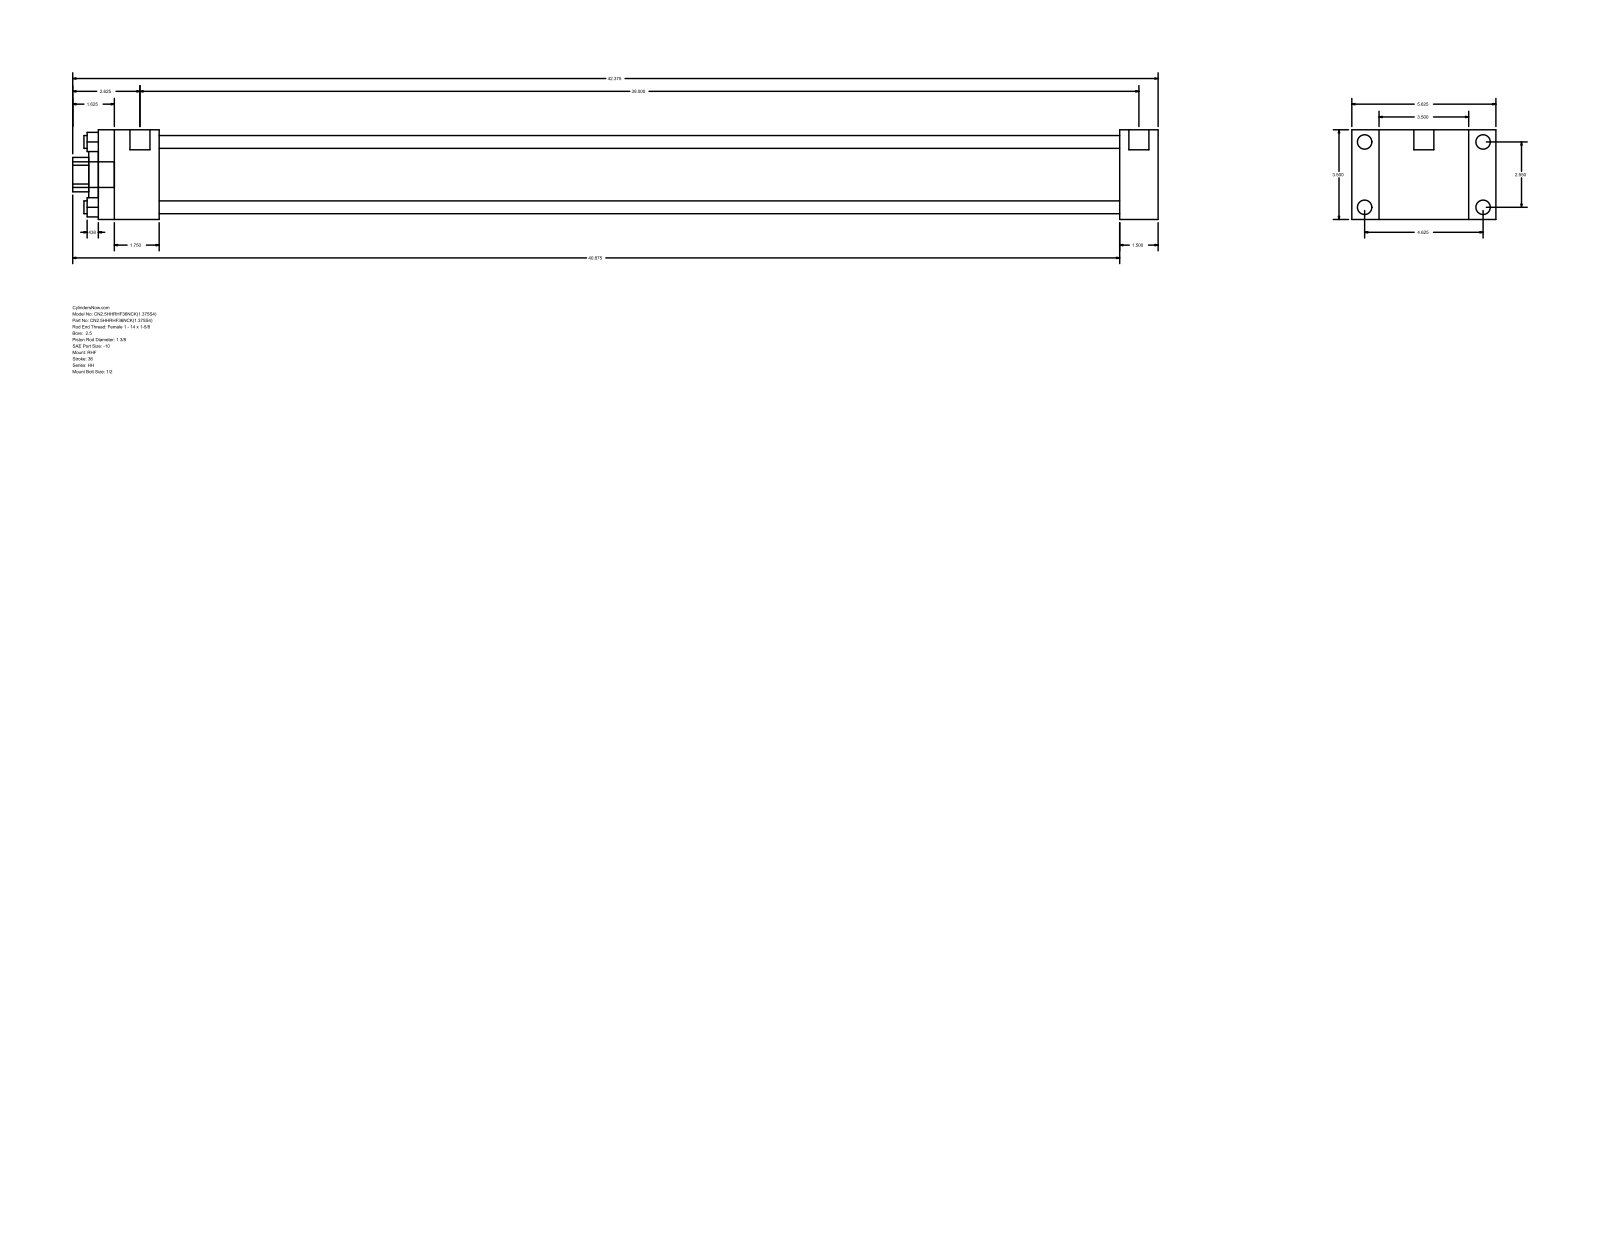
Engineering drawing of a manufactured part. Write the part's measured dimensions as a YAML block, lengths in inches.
part_name: "HH_RHF__0250_1.375"
step_written_by: "GSSL Pune (CONFIG_CONTROL_DESIGN)"
units: inches
bodies: {solids: 0, faces: 88, planar: 60, cylindrical: 28, other: 0}
overall_size: [42.375, 5.625, 3.5]
round_holes:
  - {diameter: 0.5, count: 4}
  - {diameter: 1.375, count: 1}
  - {diameter: 2, count: 1}
  - {diameter: 2.875, count: 1}
round_bosses_or_shafts:
  - {diameter: 0.563, count: 4}
  - {diameter: 0.219, count: 4}
  - {diameter: 0.781, count: 2}
  - {diameter: 1, count: 1}
partial_cylinders:
  - {radius: 0.672, count: 1}
face_to_face_distances: [3.5, 1.5, 1.063, 4.563, 39.875, 41.375, 5.625, 2.375, 37.5, 39]
hole_center_spacings: [1.803, 2.55, 3.606]
